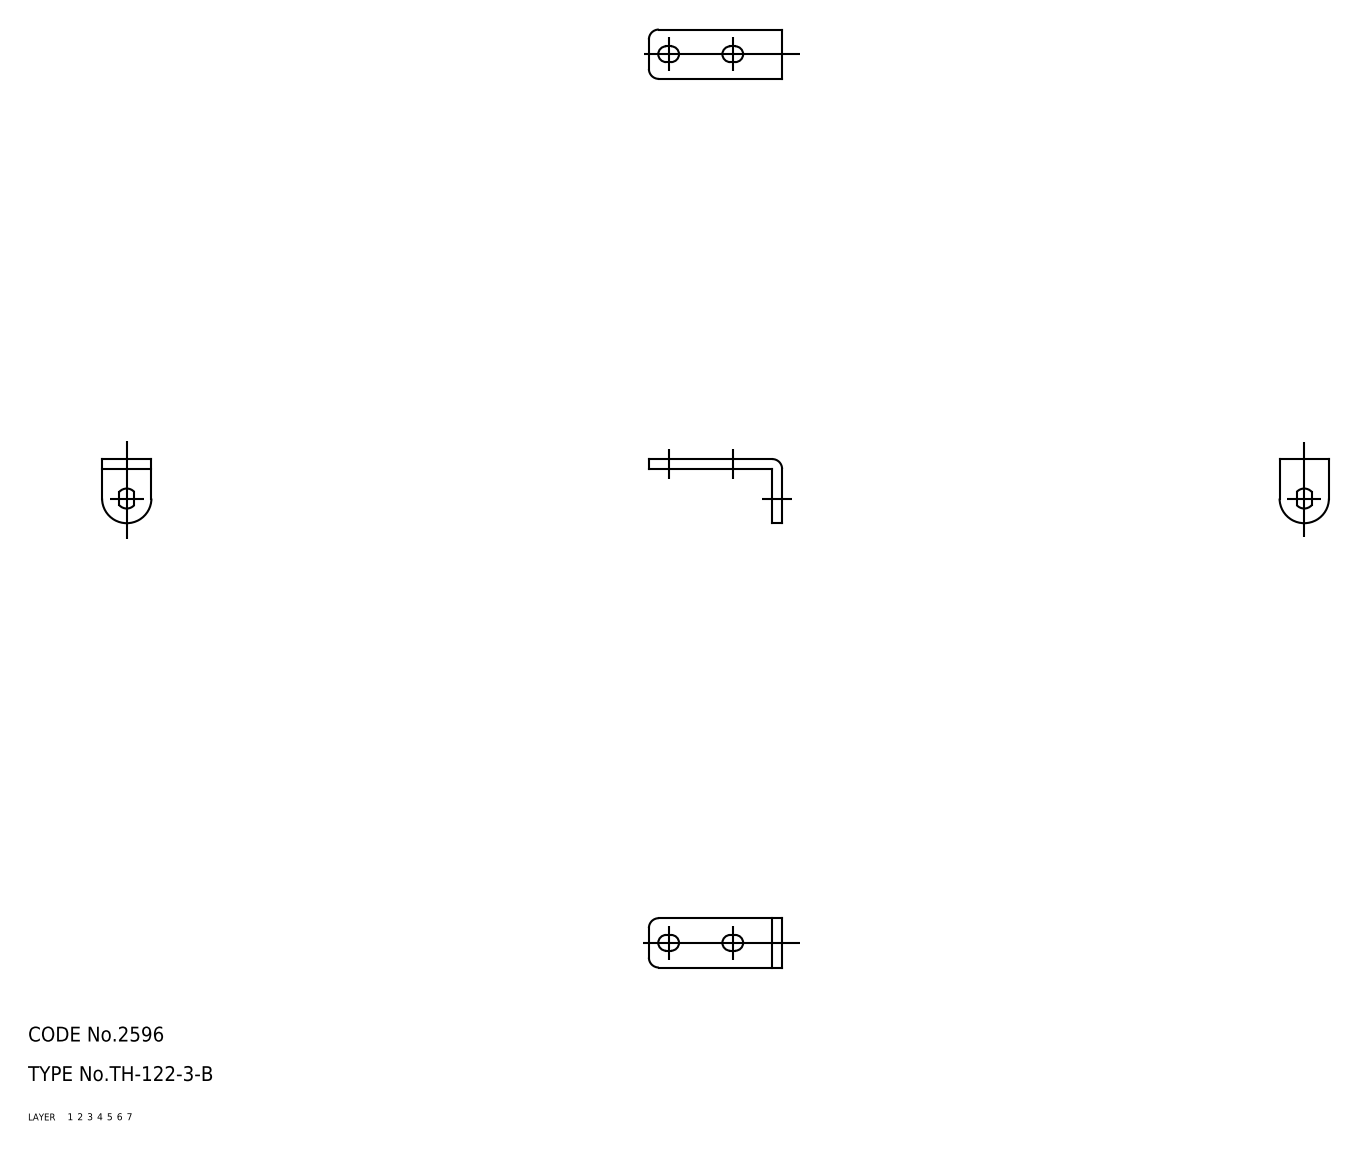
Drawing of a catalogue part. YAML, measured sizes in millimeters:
part_name: "67109940"
step_written_by: "CADfix (AUTOMOTIVE_DESIGN)"
units: millimeters
bodies: {solids: 1, faces: 23, planar: 0, cylindrical: 0, other: 23}
overall_size: [27, 13, 10]
volume: 660
surface_area: 911
